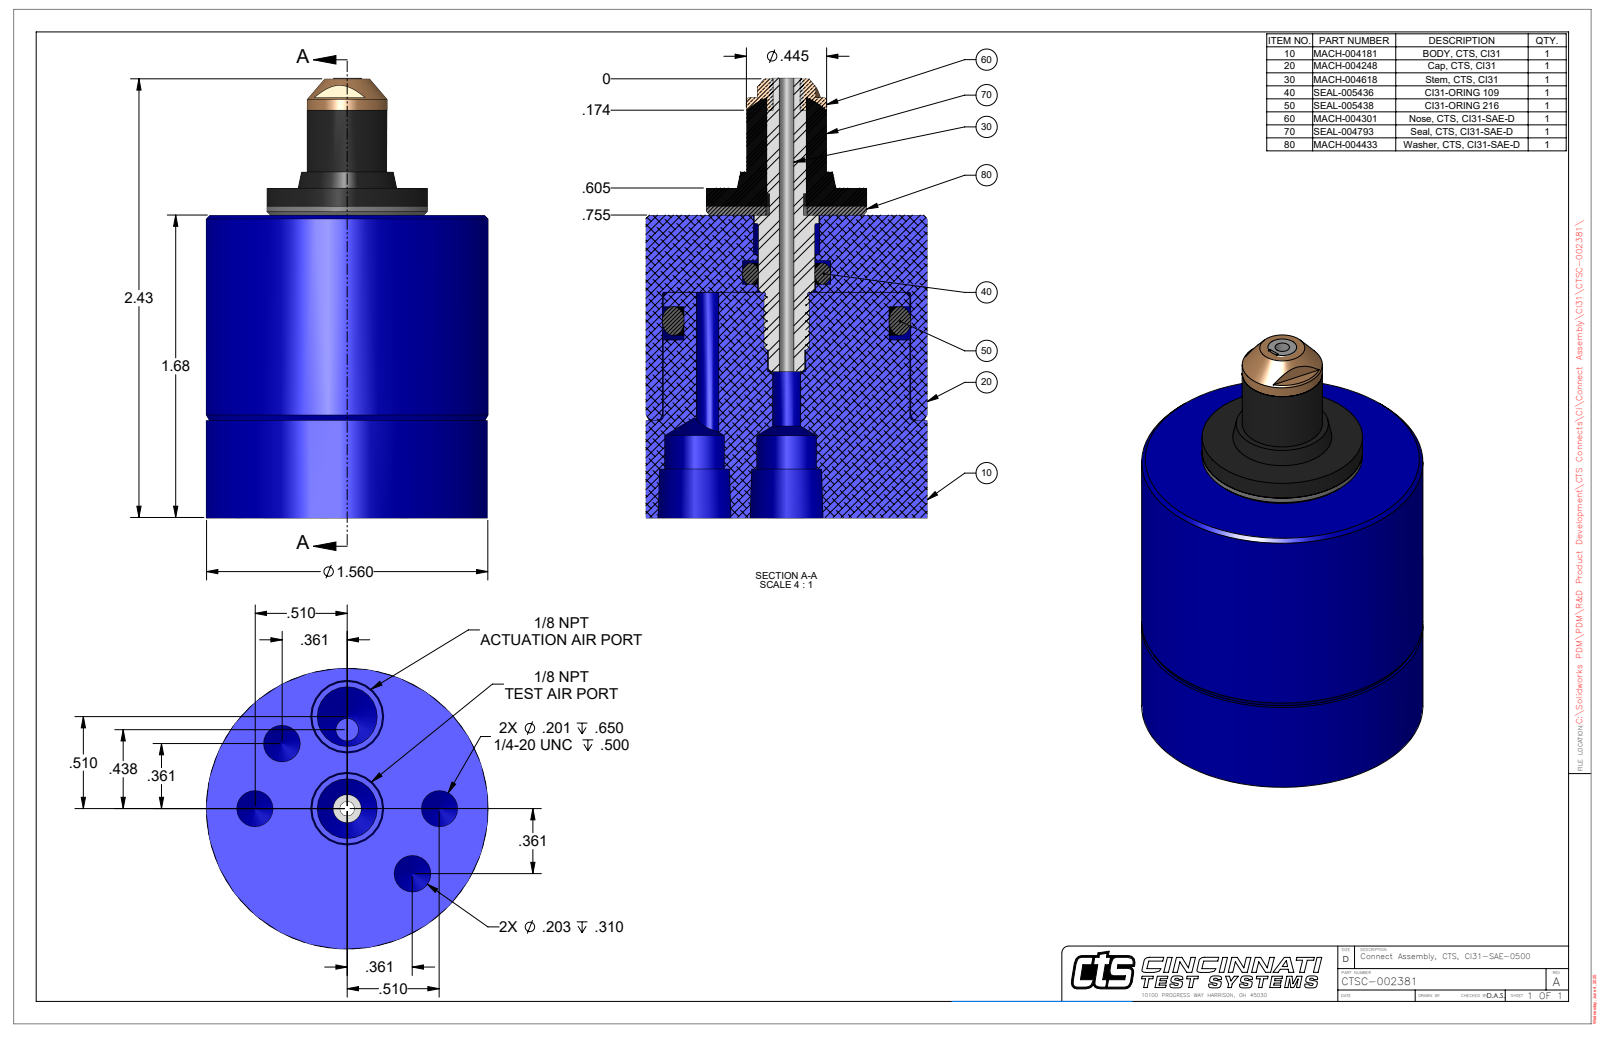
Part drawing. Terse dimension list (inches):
name: CTSC-002381
written by: SolidWorks 2023 (AUTOMOTIVE_DESIGN)
unit: in
bodies: 1 solid, 91 faces (23 planar, 36 cylindrical, 32 other)
size: 2.437 × 1.56 × 1.56
volume: 3.194 in³; area: 18.8 in²
holes: 2× ⌀0.201, 2× ⌀0.203, 2× ⌀0.332, 1× ⌀0.081, 1× ⌀0.125, 1× ⌀0.156, 1× ⌀0.368, 1× ⌀1.377
bosses: 1× ⌀1.56, 1× ⌀1.365, 1× ⌀0.89, 1× ⌀0.445, 1× ⌀0.357
rounds: 1× R0.075
face distances: 1.677, 1.827, 0.15, 0.542, 1.135, 1.285, 0.812, 0.27, 0.865, 1.015
hole spacings: 0.51, 0.39, 0.942, 0.672, 0.721, 0.072, 0.369, 0.437
